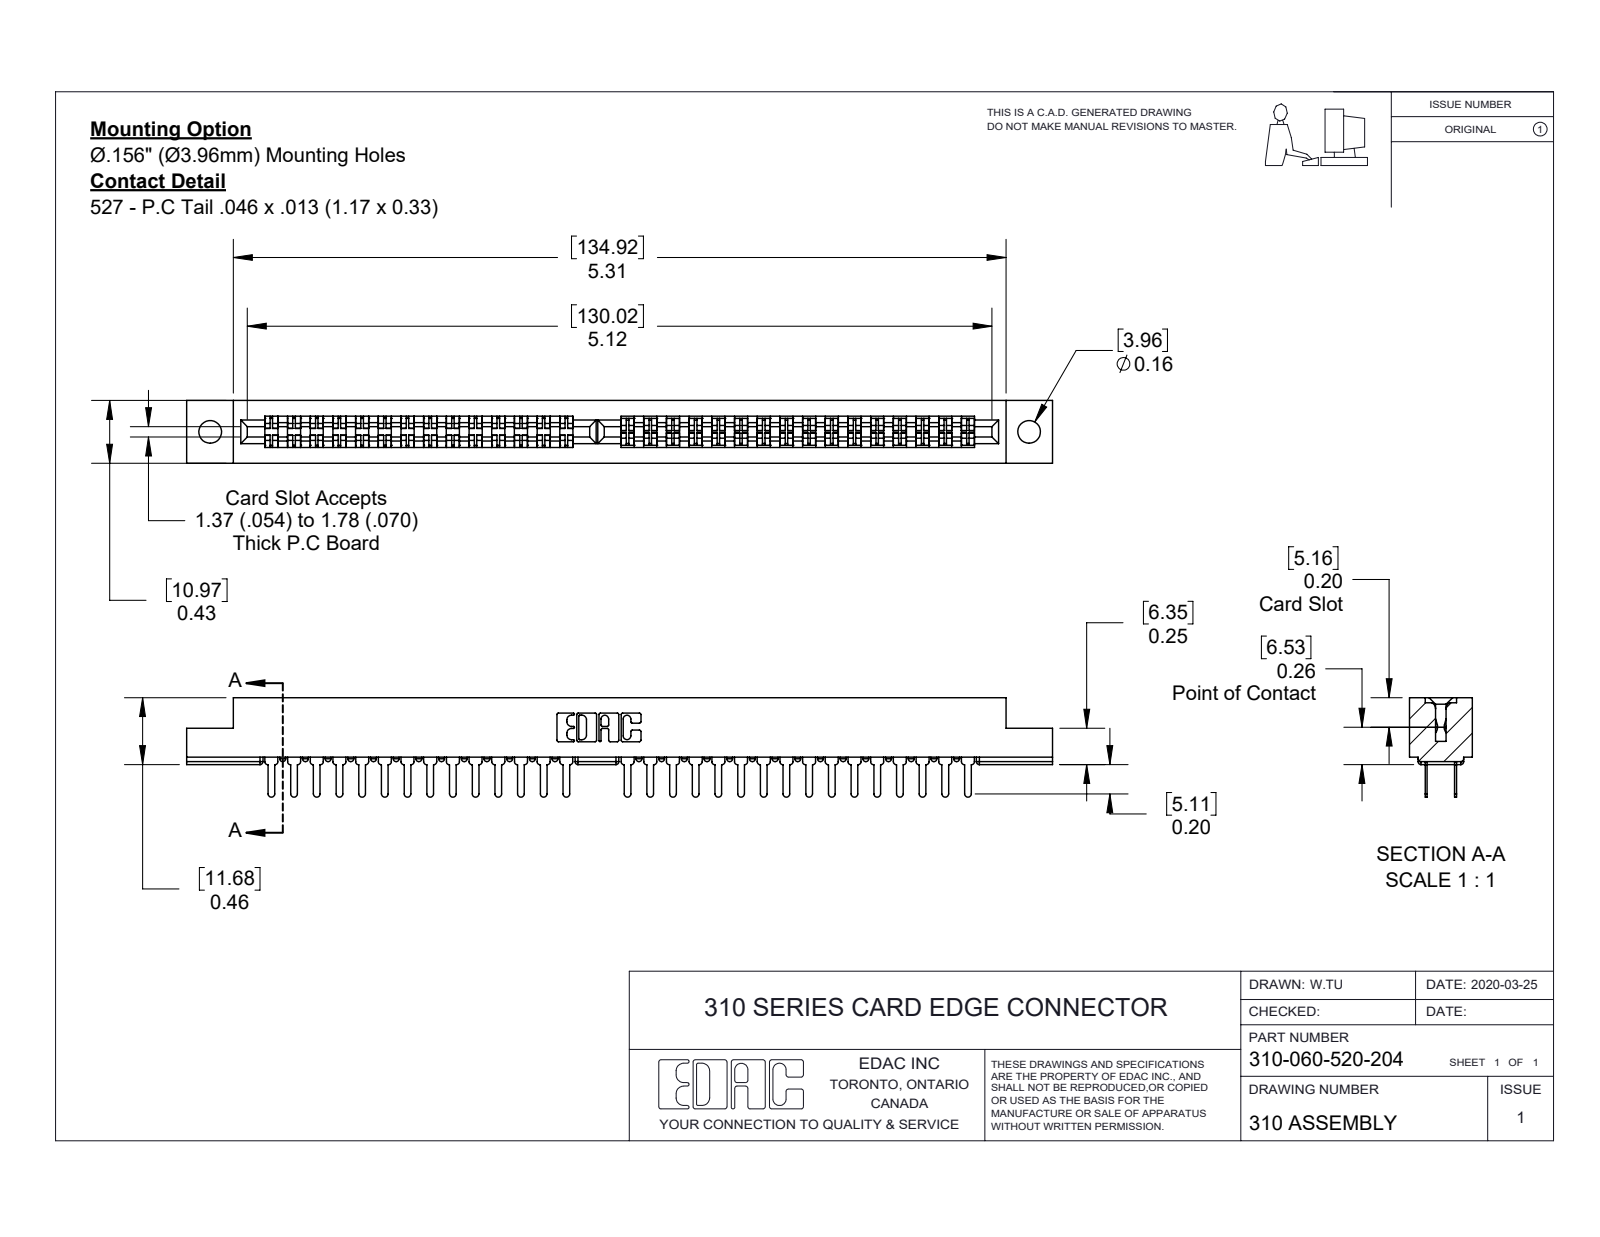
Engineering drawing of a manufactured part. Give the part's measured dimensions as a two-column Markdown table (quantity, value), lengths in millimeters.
| quantity | value |
| --- | --- |
| part name | 310 Part_.156 Dia. Hole; 307-290-001_520; 310-060-520-204 |
| STEP written by | SolidWorks 2016 (CONFIG_CONTROL_DESIGN) |
| units | millimeters |
| bodies | 61 solids, 2926 faces (1944 planar, 918 cylindrical, 64 other) |
| overall size | 151.21 × 17.37 × 10.97 |
| volume | 12 967 mm³ |
| surface area | 17 623 mm² |
| round holes (diameter × count) | 3.96 × 2 |
| partial cylindrical surfaces (radius × count) | 0.51 × 158, 0.58 × 30, 0.25 × 22, 0.17 × 6, 0.8 × 6, 0.3 × 4, 0.64 × 4, 1.19 × 4 |
| main face-to-face distances | 2.76, 8.22, 0.33, 0.38, 4.75, 10.98, 5.46, 3.14, 7.84, 5.08 |
| hole center spacings | 143 |
